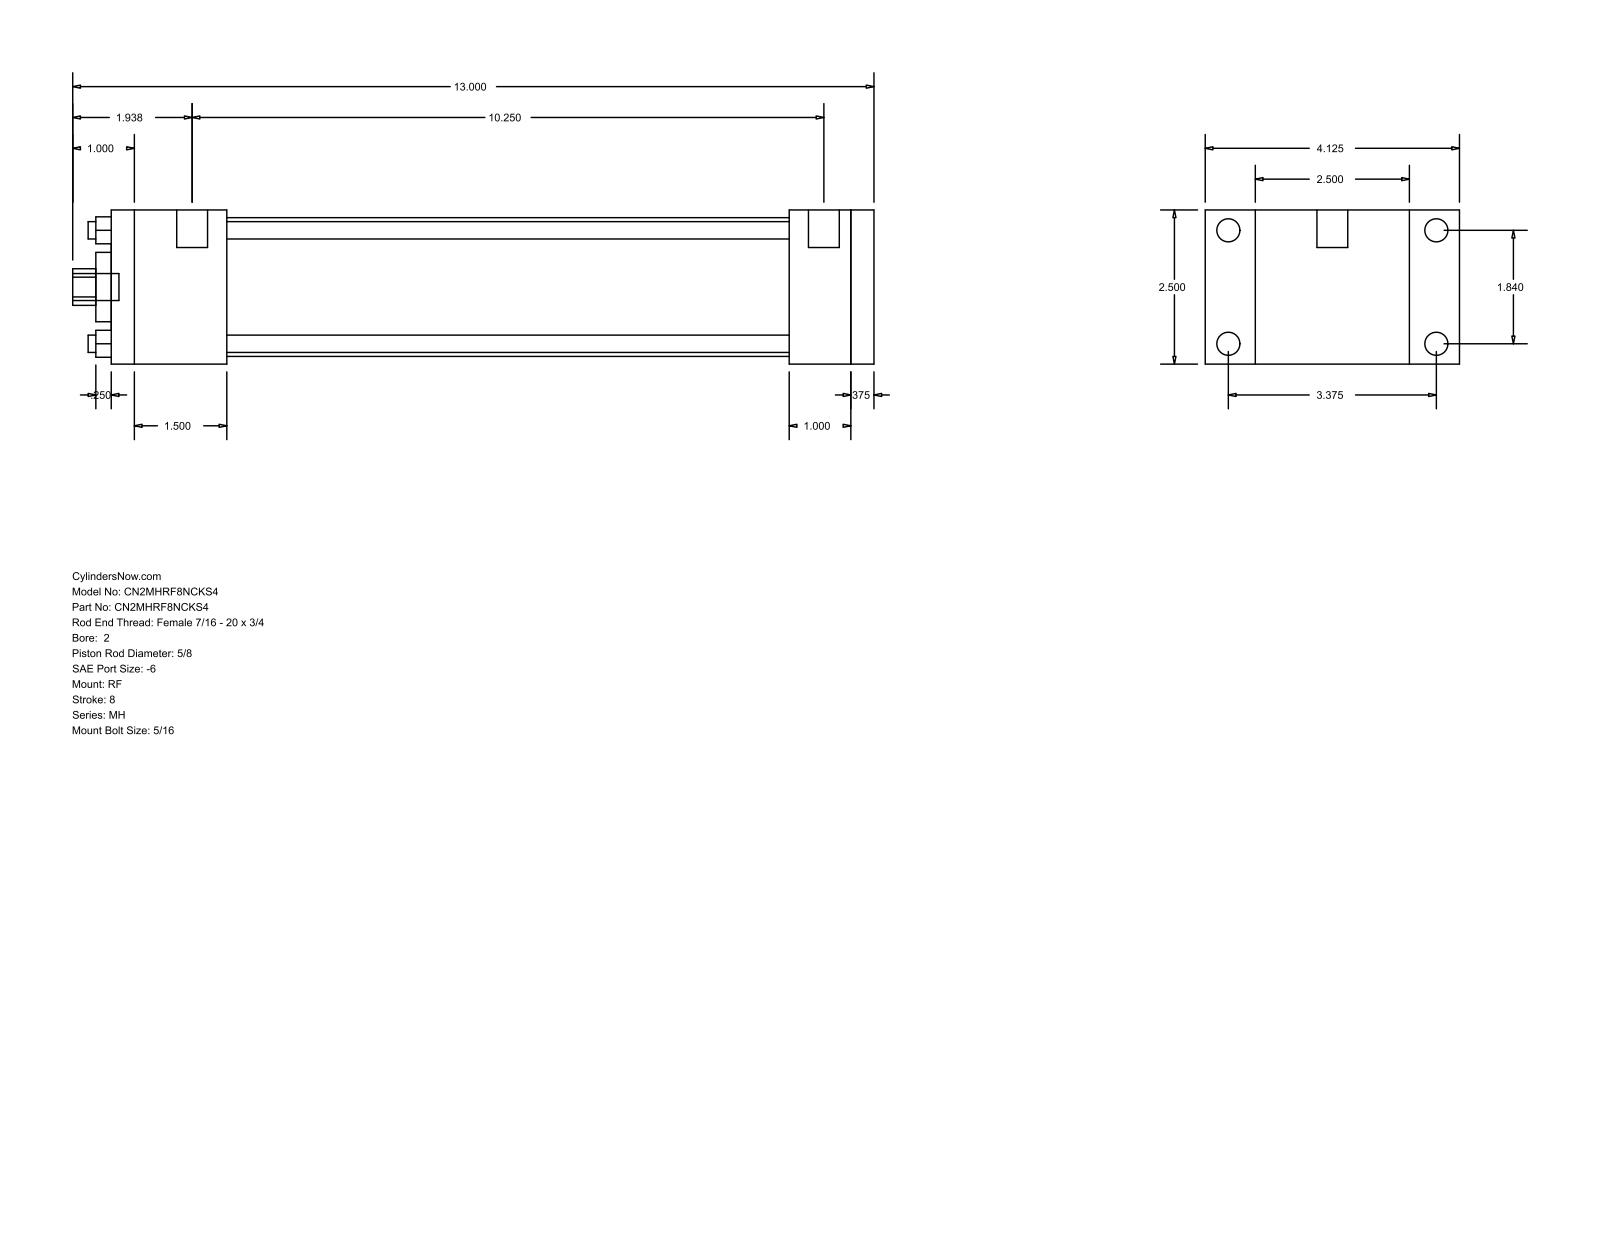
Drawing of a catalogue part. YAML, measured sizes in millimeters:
part_name: "MH_RF__0200_0.625"
step_written_by: "GSSL Pune (CONFIG_CONTROL_DESIGN)"
units: millimeters
bodies: {solids: 0, faces: 92, planar: 64, cylindrical: 28, other: 0}
overall_size: [330.2, 104.78, 63.5]
round_holes:
  - {diameter: 7.14, count: 4}
  - {diameter: 15.88, count: 1}
  - {diameter: 28.57, count: 1}
  - {diameter: 57.15, count: 1}
round_bosses_or_shafts:
  - {diameter: 9.53, count: 4}
  - {diameter: 5.56, count: 4}
  - {diameter: 12.7, count: 2}
  - {diameter: 11.11, count: 1}
partial_cylinders:
  - {radius: 7.54, count: 1}
face_to_face_distances: [63.5, 314.32, 9.52, 304.8, 47.62, 279.39, 231.77, 257.18, 266.7, 25.41]
hole_center_spacings: [33.05, 46.74, 66.1]
